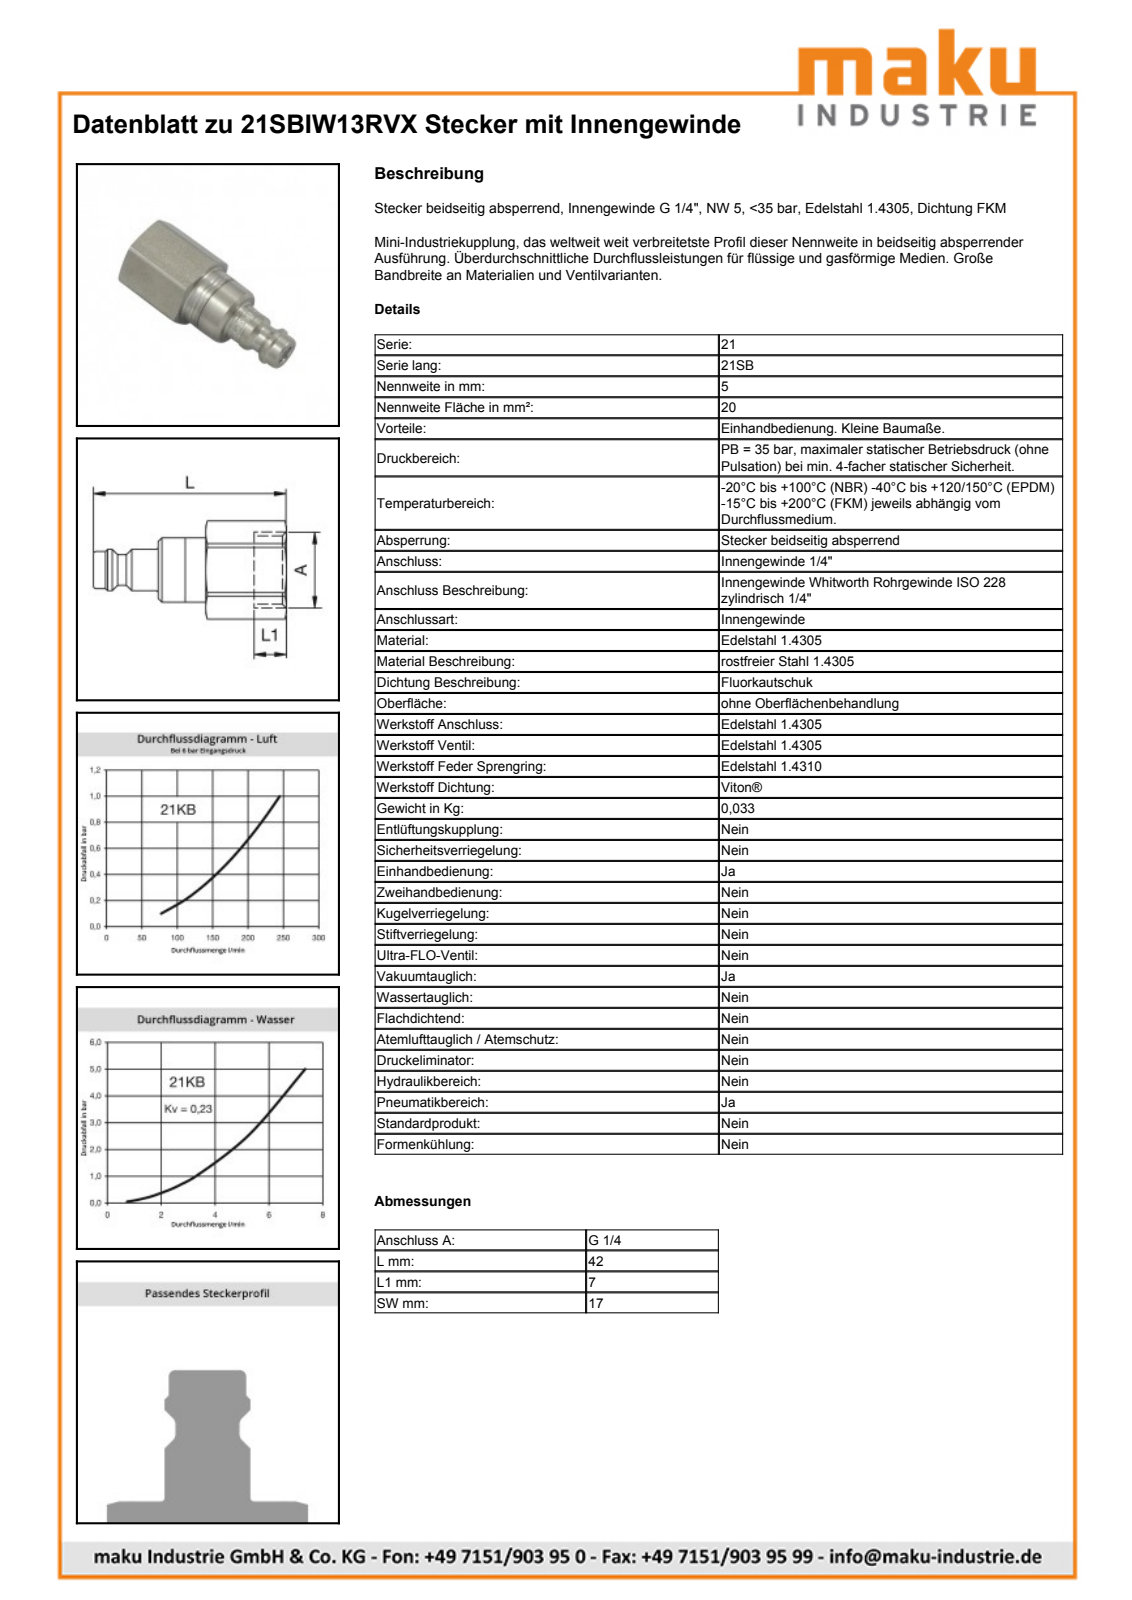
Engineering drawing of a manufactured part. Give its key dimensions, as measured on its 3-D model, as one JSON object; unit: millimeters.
{"part_name": "D106122", "step_written_by": "Autodesk Inventor 2011 (AUTOMOTIVE_DESIGN)", "units": "millimeters", "bodies": {"solids": 1, "faces": 55, "planar": 14, "cylindrical": 17, "other": 24}, "overall_size": [42, 18.73, 18.68], "volume_mm3": 5786, "surface_area_mm2": 2871, "round_holes": [[7.5, 1], [11.45, 1], [12, 1]], "round_bosses_or_shafts": [[14, 1], [11.94, 1], [9, 1], [8.1, 1], [6.7, 1]], "partial_cylinders_radius": [[9.57, 1]], "face_to_face_distances": [17, 17.55, 8.55, 9, 8.53, 9.02, 10.35, 18.88, 18.9, 27.9]}
